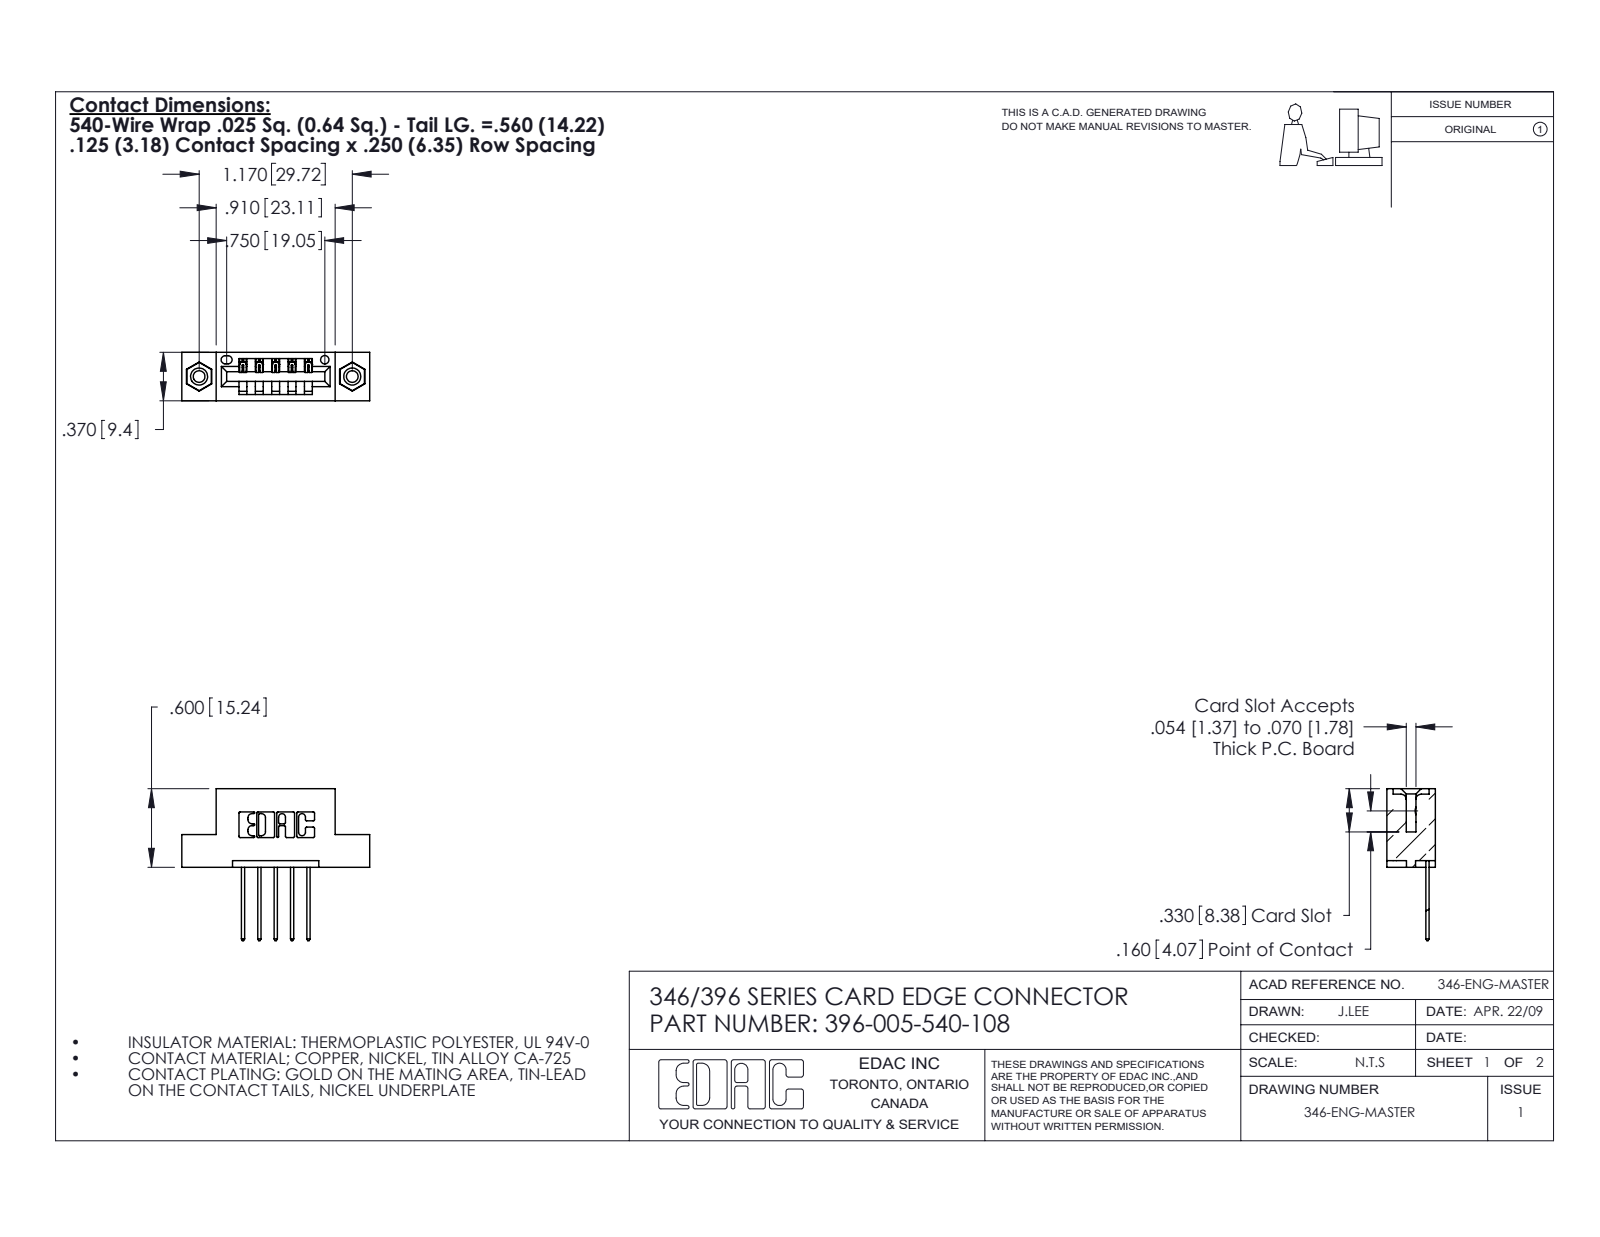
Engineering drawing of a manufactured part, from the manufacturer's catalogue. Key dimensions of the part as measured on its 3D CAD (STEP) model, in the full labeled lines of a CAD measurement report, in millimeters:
Part name (STEP PRODUCT): 346 Part_Flush Mounting Lugs - 0.156 Dia-TI; 345-292-001_345-293-140; 396-005-540-108; 345-250-001_345-250-003-102
STEP written by: SolidWorks 2020 (CONFIG_CONTROL_DESIGN)
Units: millimetres
Bodies: 8 solids, 472 faces (308 planar, 148 cylindrical, 16 other)
Overall size (bounding box): 36.4 × 29.5 × 9.4
Volume: 3 230 mm³ · Surface area: 3 714 mm²
Round holes (diameter × count): ⌀2.3 ×2, ⌀3.2 ×2, ⌀4 ×2, ⌀1.6 ×1
Round bosses / shafts (diameter × count): ⌀3.9 ×2
Partial cylindrical surfaces — rounded edges, fillets, slot ends (radius × count): R0.3 ×22, R0.2 ×10, R0.3 ×10, R0.2 ×6, R0.8 ×6, R0.7 ×3, R0.8 ×2, R1 ×2
Main face-to-face distances: 6.4, 9.4, 1.2, 8.2, 1.8, 7.6, 0.6, 14, 3.8, 5.6
Hole centre spacings: 6.2, 24.6, 29.7
